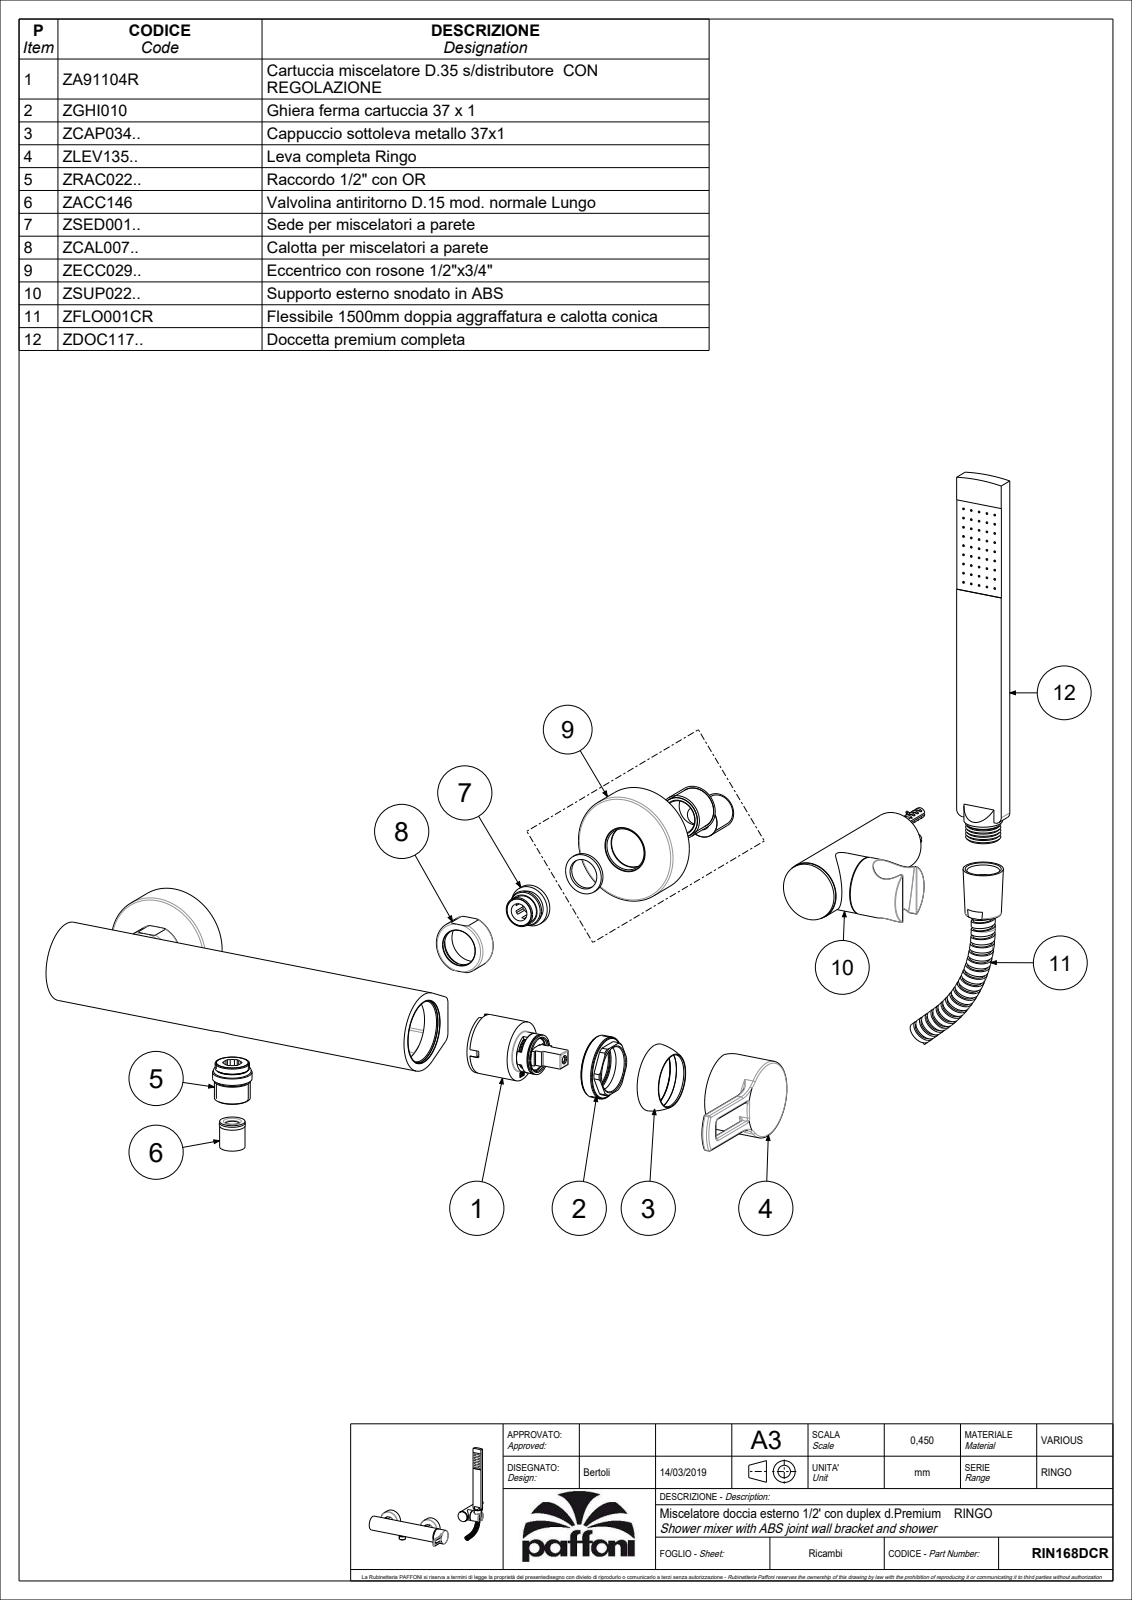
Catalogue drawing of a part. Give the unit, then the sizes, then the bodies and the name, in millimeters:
Units: millimetres
Overall size (bounding box): 419.75 × 372.95 × 132.95
Round holes (diameter × count): ⌀7 ×3, ⌀20 ×3, ⌀3.5 ×2, ⌀4 ×2, ⌀7.8 ×2, ⌀9.5 ×2, ⌀10.5 ×2, ⌀16 ×2, ⌀18 ×2, ⌀21.6 ×2, ⌀29 ×2, ⌀62.3 ×2
Round bosses / shafts (diameter × count): ⌀2 ×11, ⌀6.9 ×3, ⌀3.9 ×3, ⌀63.5 ×2, ⌀27 ×2, ⌀26.2 ×2, ⌀23 ×2, ⌀20.5 ×2
Partial cylindrical surfaces — rounded edges, fillets, slot ends (radius × count): R1.5 ×44, R0.5 ×34, R1 ×14, R0.15 ×11, R0.3 ×10, R2 ×6, R5 ×6, R1.3 ×4
Main face-to-face distances: 3.7, 10, 50.5, 0.6, 51.1, 61.1, 60.5, 34.8, 3.5, 35.5
Hole centre spacings: 7.07, 8.6, 11.4, 150, 4, 6, 10, 11
Volume: 391 147 mm³ · Surface area: 238 570 mm²
Bodies: 6 solids, 2152 faces (1134 planar, 551 cylindrical, 467 other)
Part name (STEP PRODUCT): RIN168DCR
STEP written by: CREO PARAMETRIC BY PTC INC, 2020044 (CONFIG_CONTROL_DESIGN)
